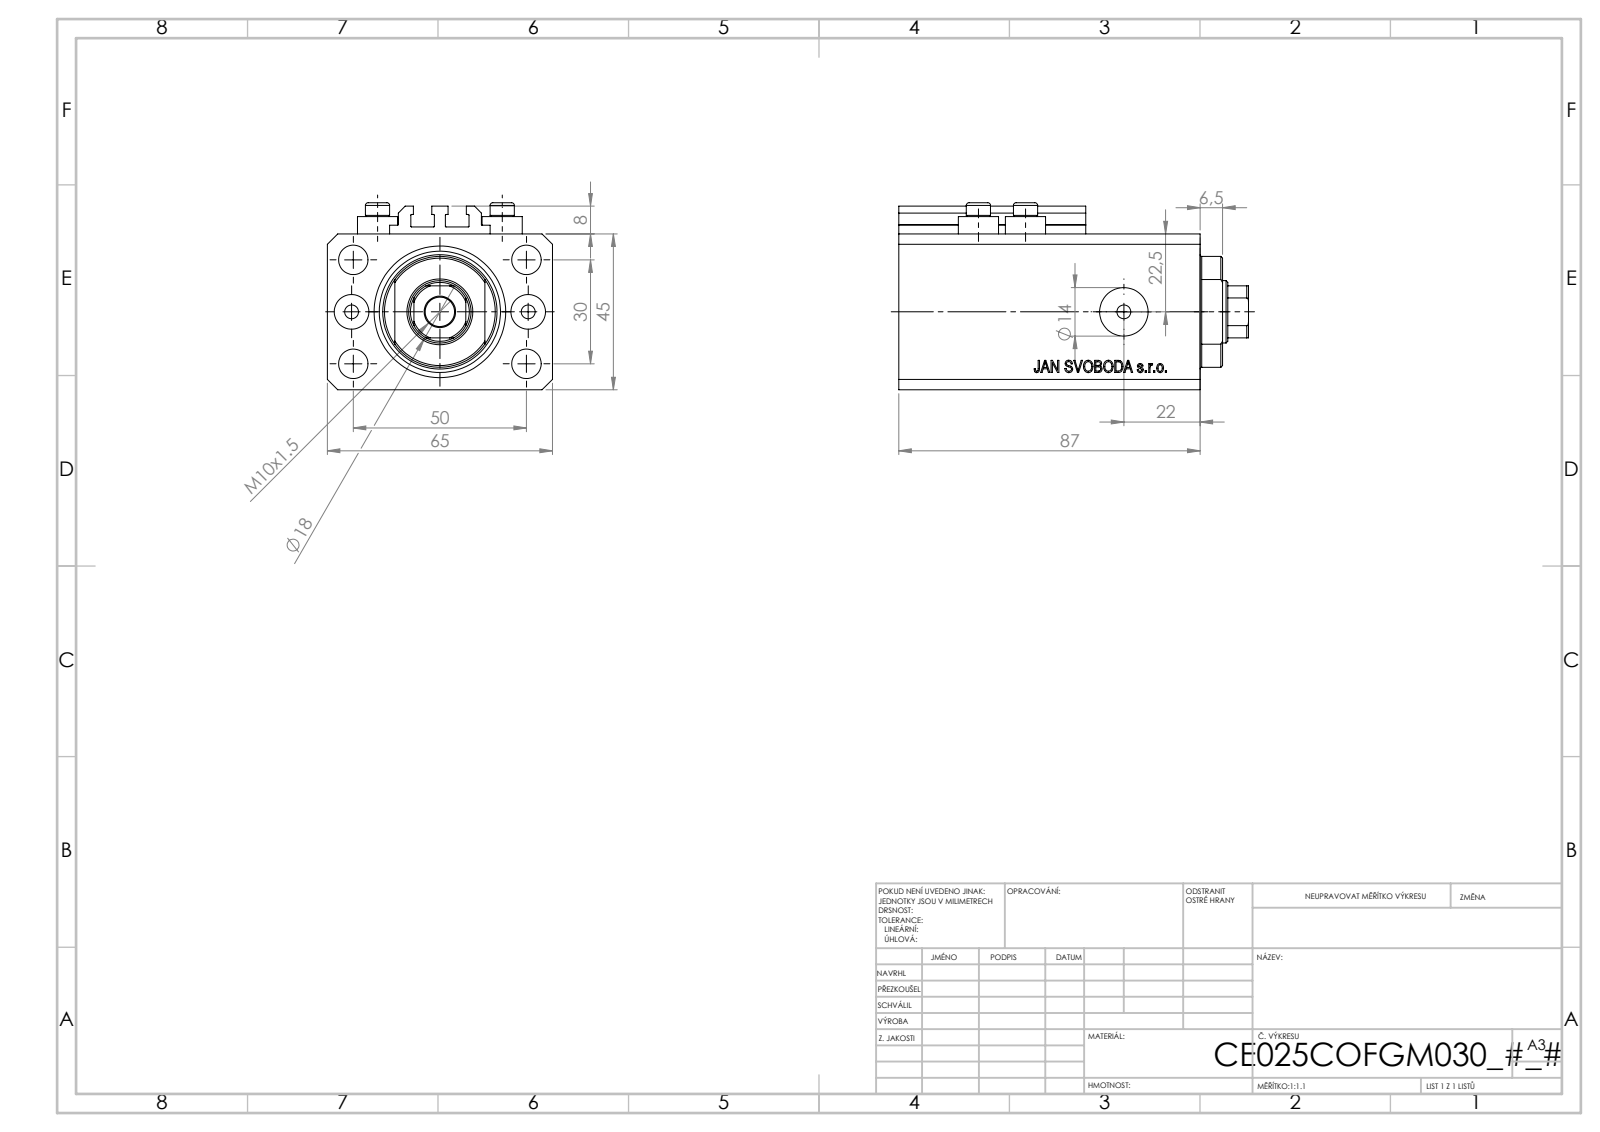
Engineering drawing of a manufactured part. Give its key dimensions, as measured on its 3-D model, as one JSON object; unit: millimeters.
{"part_name": "V250CE_C_Body; V250CE_C_VCP; ALLEN BOLT V250CE; V250CE_VC_C", "step_written_by": "SolidWorks 2019 (CONFIG_CONTROL_DESIGN)", "units": "millimeters", "bodies": {"solids": 8, "faces": 1034, "planar": 504, "cylindrical": 86, "other": 444}, "overall_size": [101, 65, 54], "volume_mm3": 237637, "surface_area_mm2": 62822, "round_holes": [[4, 8], [8.5, 5], [10, 2], [14, 2], [18, 1], [25, 1], [38, 1]], "round_bosses_or_shafts": [[11.6, 4], [7, 4]], "partial_cylinders_radius": [[0.2, 10], [8.5, 1], [16, 1]], "face_to_face_distances": [45, 65, 14, 73, 87, 47, 6.9, 66.1, 80.1, 3], "hole_center_spacings": [15.01, 29.15, 52.68, 13.6, 25.5, 30, 36, 38.48]}
